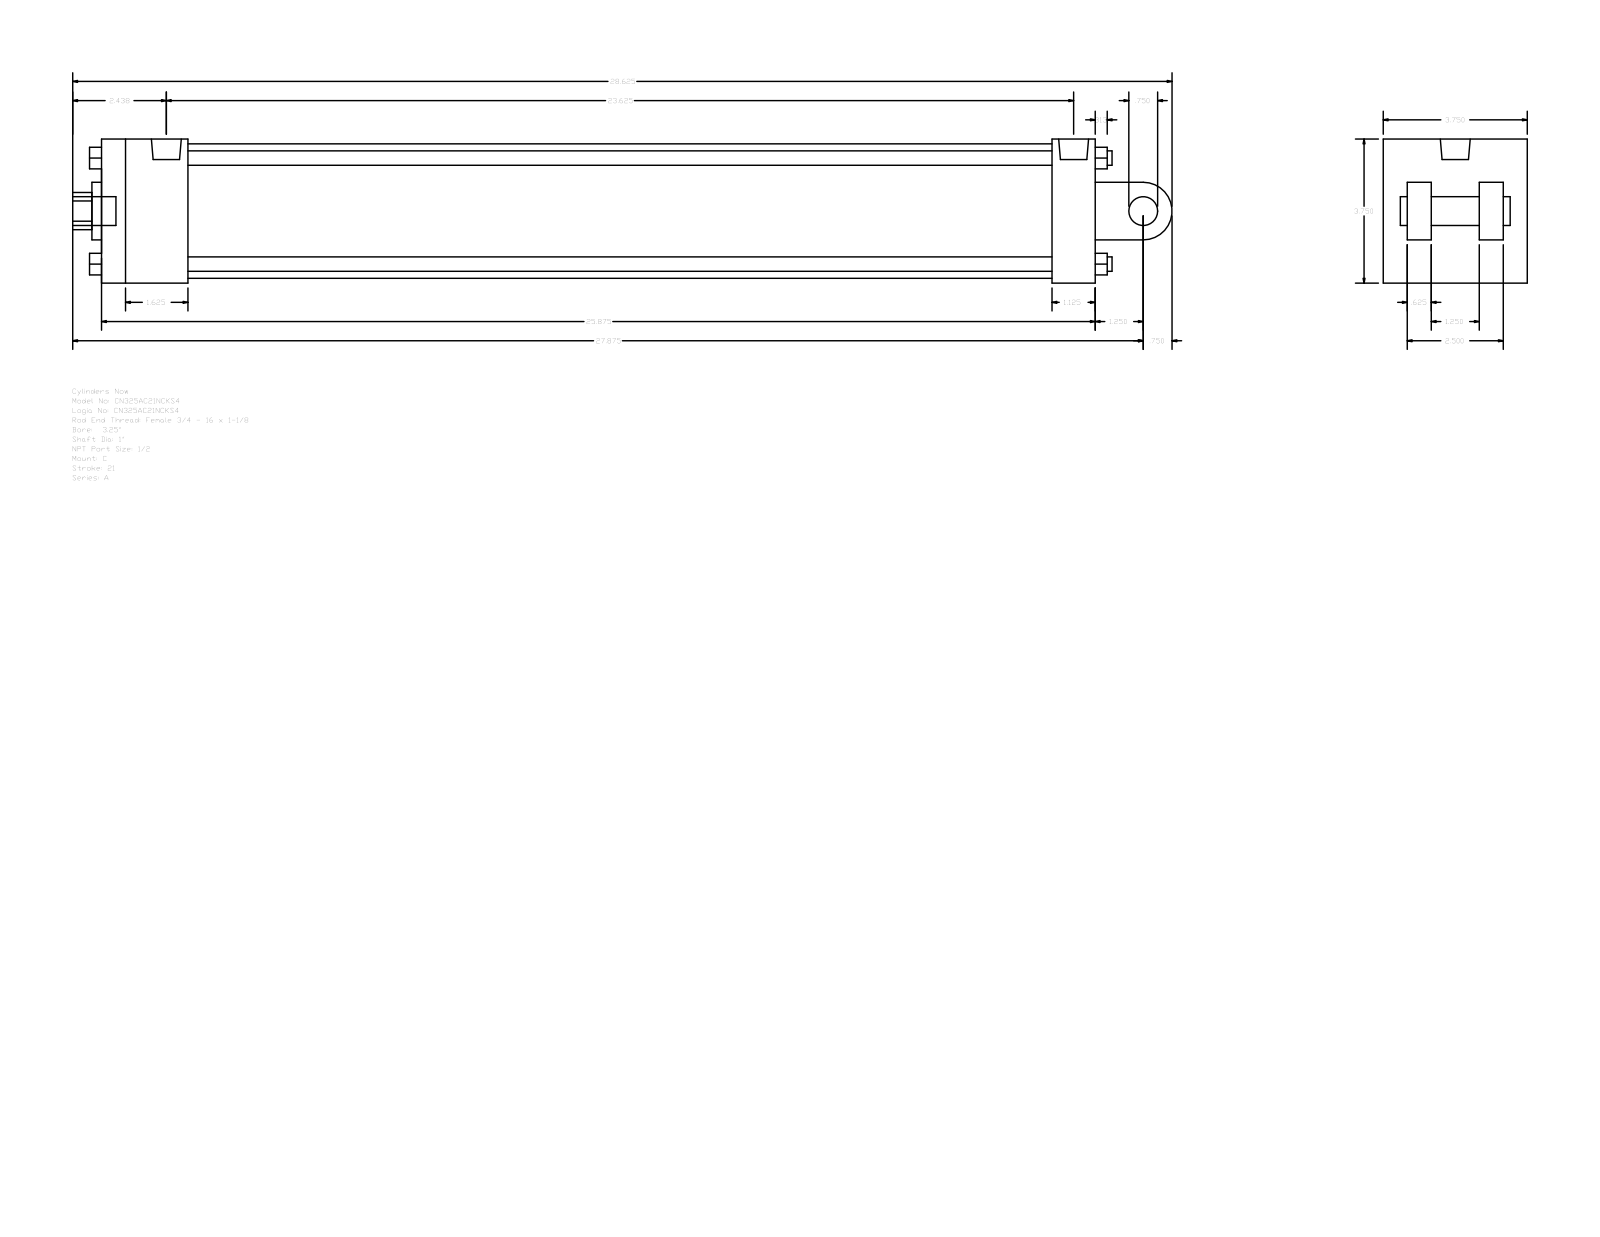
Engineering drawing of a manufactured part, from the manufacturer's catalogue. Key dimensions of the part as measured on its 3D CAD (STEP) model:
Part name (STEP PRODUCT): A_C__0325_1
STEP written by: GSSL Pune (CONFIG_CONTROL_DESIGN)
Units: millimetres
Bodies: 0 solids, 135 faces (102 planar, 33 cylindrical, 0 other)
Overall size (bounding box): 727.08 × 95.25 × 95.25
Round holes (diameter × count): ⌀8.73 ×2, ⌀19.77 ×1, ⌀25.4 ×1, ⌀38.1 ×1, ⌀88.9 ×1
Round bosses / shafts (diameter × count): ⌀9.53 ×4, ⌀19.05 ×2, ⌀8.73 ×2, ⌀19.77 ×1
Partial cylindrical surfaces — rounded edges, fillets, slot ends (radius × count): R12.29 ×1, R19.05 ×1
Main face-to-face distances: 95.24, 657.22, 15.87, 63.5, 28.57, 47.63, 31.74, 79.37, 66.67, 628.65
Hole centre spacings: 3.18
